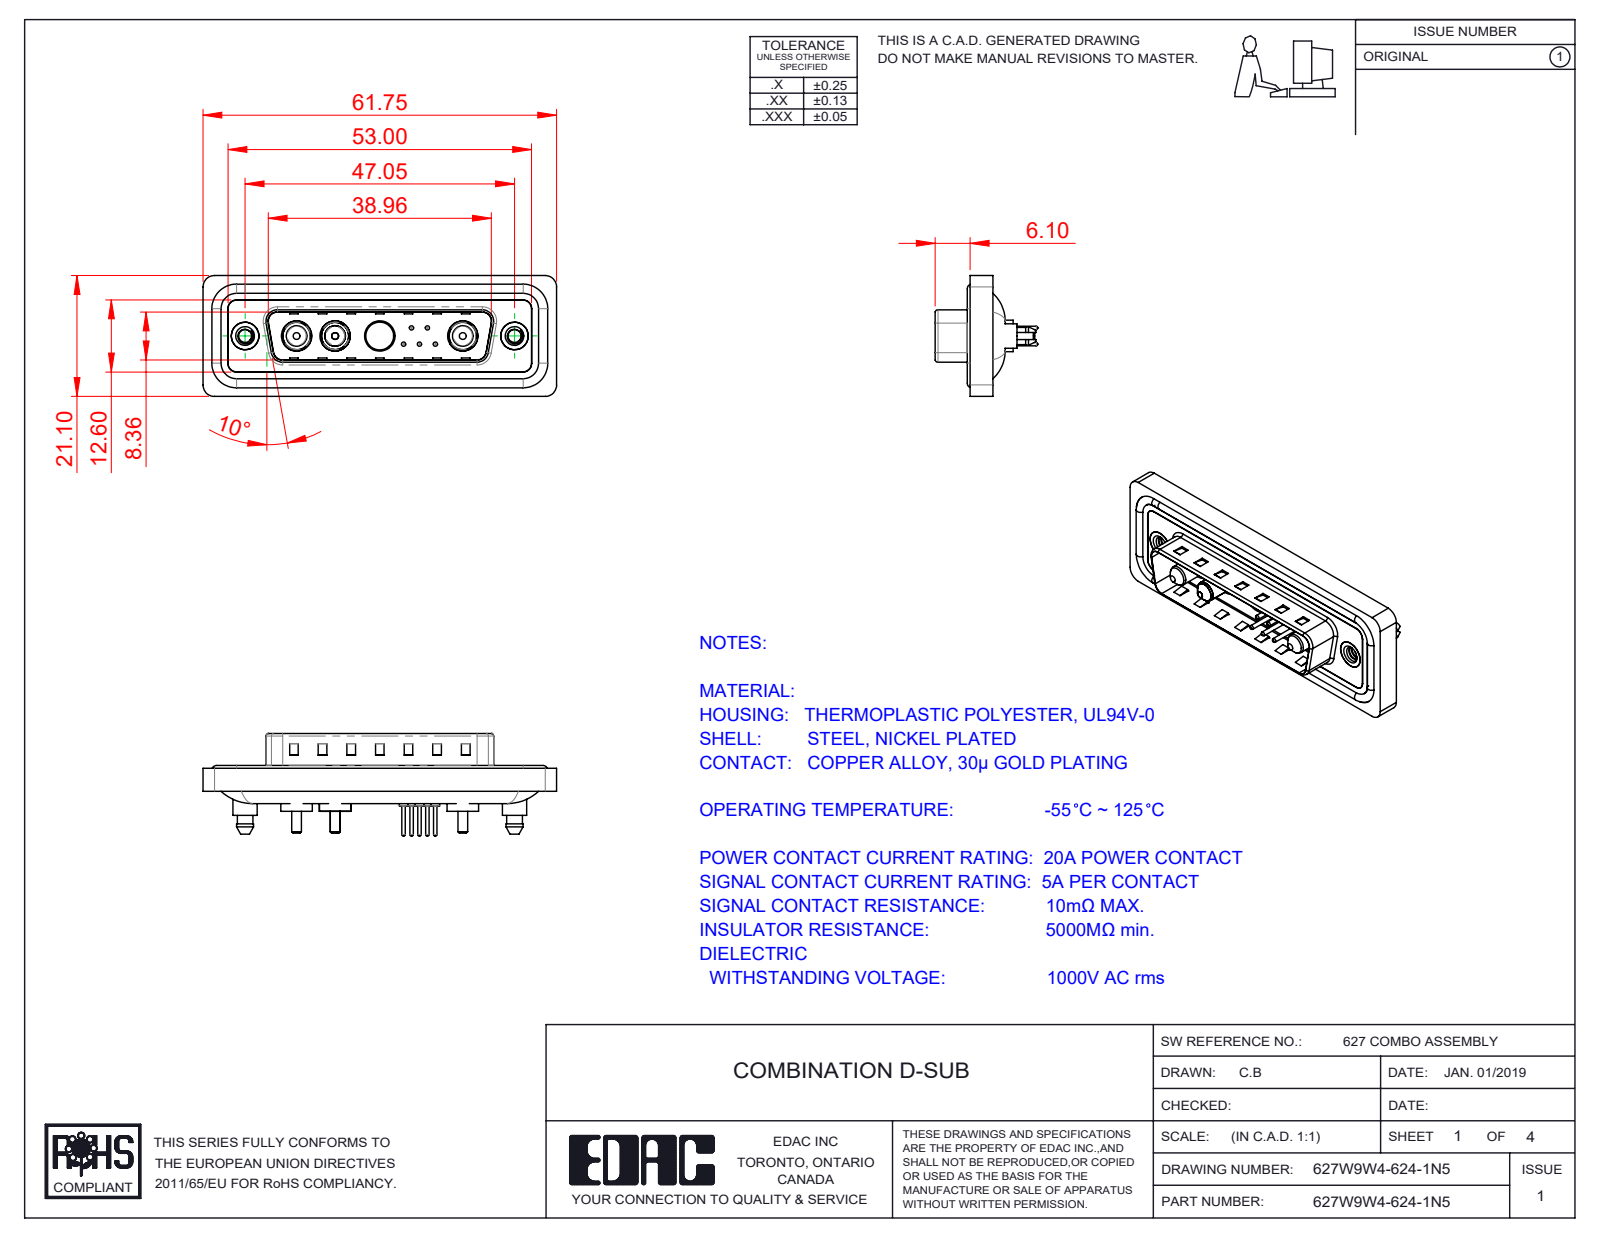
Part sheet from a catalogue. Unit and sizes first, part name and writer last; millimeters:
Units: millimetres
Overall size (bounding box): 61.75 × 21.1 × 17.9
Round holes (diameter × count): ⌀0.75 ×5, ⌀1.6 ×5, ⌀2 ×5, ⌀4.85 ×4, ⌀5.3 ×4, ⌀2.26 ×2, ⌀4 ×2, ⌀4.8 ×2, ⌀5 ×2
Round bosses / shafts (diameter × count): ⌀1.5 ×5, ⌀0.6 ×5, ⌀1.6 ×4, ⌀5.5 ×3, ⌀5.2 ×3, ⌀4.75 ×3, ⌀3.75 ×3, ⌀3.6 ×3
Partial cylindrical surfaces — rounded edges, fillets, slot ends (radius × count): R1.5 ×24, R2 ×18, R1.6 ×10, R0.5 ×8, R0.25 ×4, R0.6 ×4, R0.65 ×4, R0.9 ×4
Main face-to-face distances: 0.4, 1.5, 1.1, 0.5, 1.6, 3.1, 2.9, 0.82, 9.58, 5.65
Hole centre spacings: 3.16, 2.77, 5.04, 14.51, 2.78, 4.4, 4.41, 5
Volume: 7 479 mm³ · Surface area: 12 118 mm²
Bodies: 20 solids, 874 faces (300 planar, 366 cylindrical, 208 other)
Part name (STEP PRODUCT): 627Combo Shell Rear_25 Contacts; 627Combo Contact Row 2_24; 627Combo Shell Front_25 Contacts; 627Combo Waterproof Housing_25 Contacts (+5 more)
STEP written by: SolidWorks 2020 (CONFIG_CONTROL_DESIGN)
